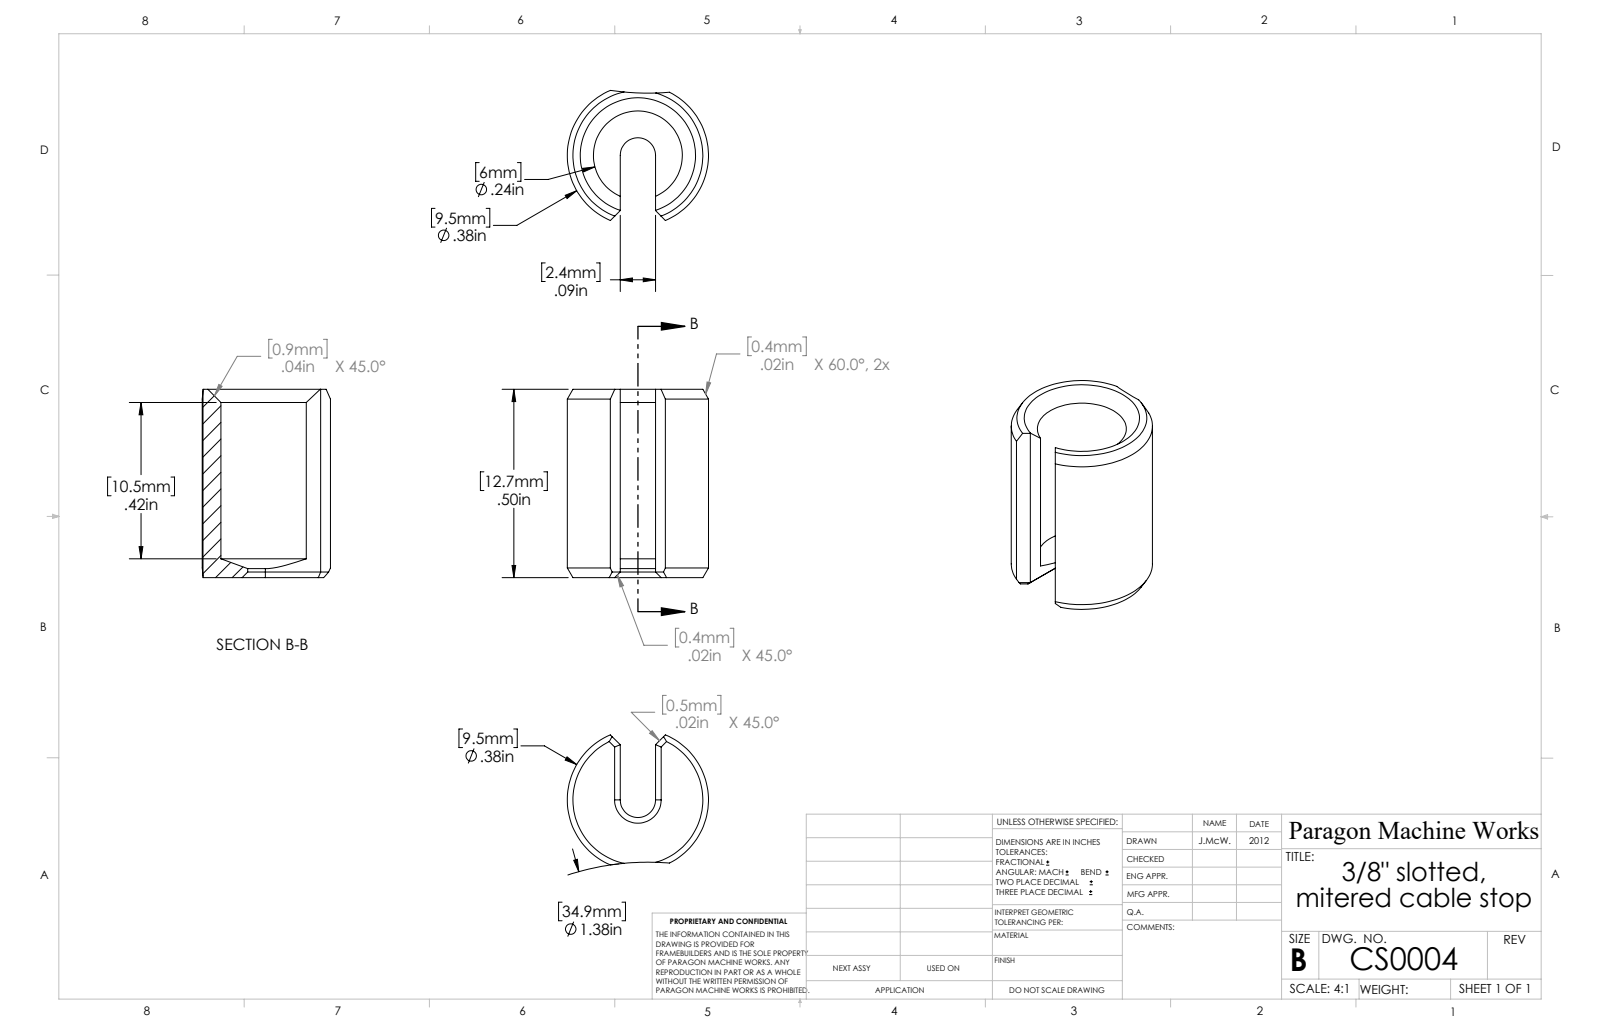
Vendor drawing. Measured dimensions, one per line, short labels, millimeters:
name: CS0004
written by: SolidWorks 2012 (AUTOMOTIVE_DESIGN)
unit: mm
bodies: 1 solid, 22 faces (10 planar, 5 cylindrical, 7 other)
size: 12.7 × 9.5 × 8.8
volume: 480 mm³; area: 661 mm²
holes: 1× ⌀6
rounds: 1× R1.2, 1× R4.8, 1× R17.4
face distances: 2.4, 12.7
